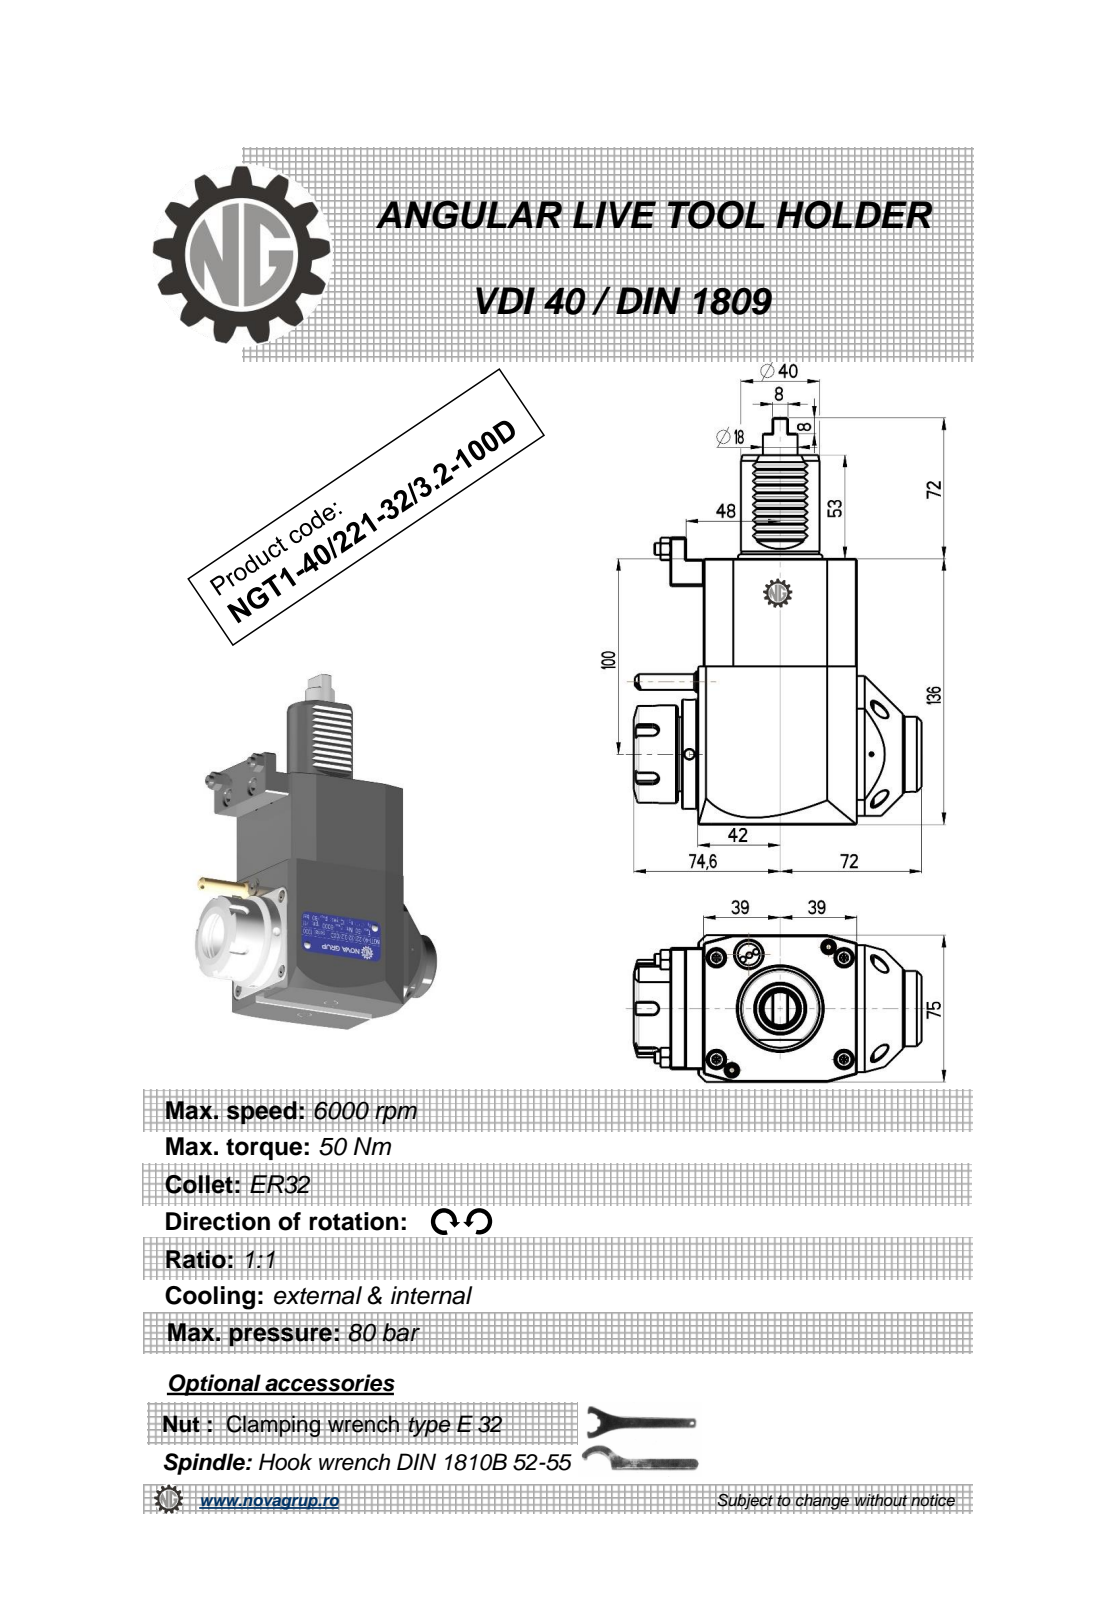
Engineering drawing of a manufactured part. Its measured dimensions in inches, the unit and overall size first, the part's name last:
Units: inches
Overall size (bounding box): 8.189 × 5.772 × 2.953
Round holes (diameter × count): ⌀0.13 ×4, ⌀0.177 ×4, ⌀0.315 ×4, ⌀0.197 ×3, ⌀0.118 ×1, ⌀1.063 ×1
Round bosses / shafts (diameter × count): ⌀0.236 ×2, ⌀2.205 ×1, ⌀1.969 ×1, ⌀1.693 ×1, ⌀1.575 ×1, ⌀1.516 ×1, ⌀0.701 ×1, ⌀0.441 ×1
Partial cylindrical surfaces — rounded edges, fillets, slot ends (radius × count): R0.012 ×10, R0.012 ×10, R0.009 ×6, R0.118 ×5, R0.031 ×2, R0.02 ×1, R1.575 ×1
Main face-to-face distances: 2.953, 5.354, 3.071, 0.551, 3.189, 0.02, 0.118, 4.803, 0.315, 0.433
Hole centre spacings: 1.26, 1.782, 2.52, 0.601, 1.611, 1.678, 2.356, 2.83
Volume: 62.67 in³ · Surface area: 125.1 in²
Bodies: 1 solid, 445 faces (181 planar, 99 cylindrical, 165 other)
Part name (STEP PRODUCT): NGT1_40_221_32_3_2_100D
STEP written by: PRO/ENGINEER BY PARAMETRIC TECHNOLOGY CORPORATION, 2010280 (CONFIG_CONTROL_DESIGN)
